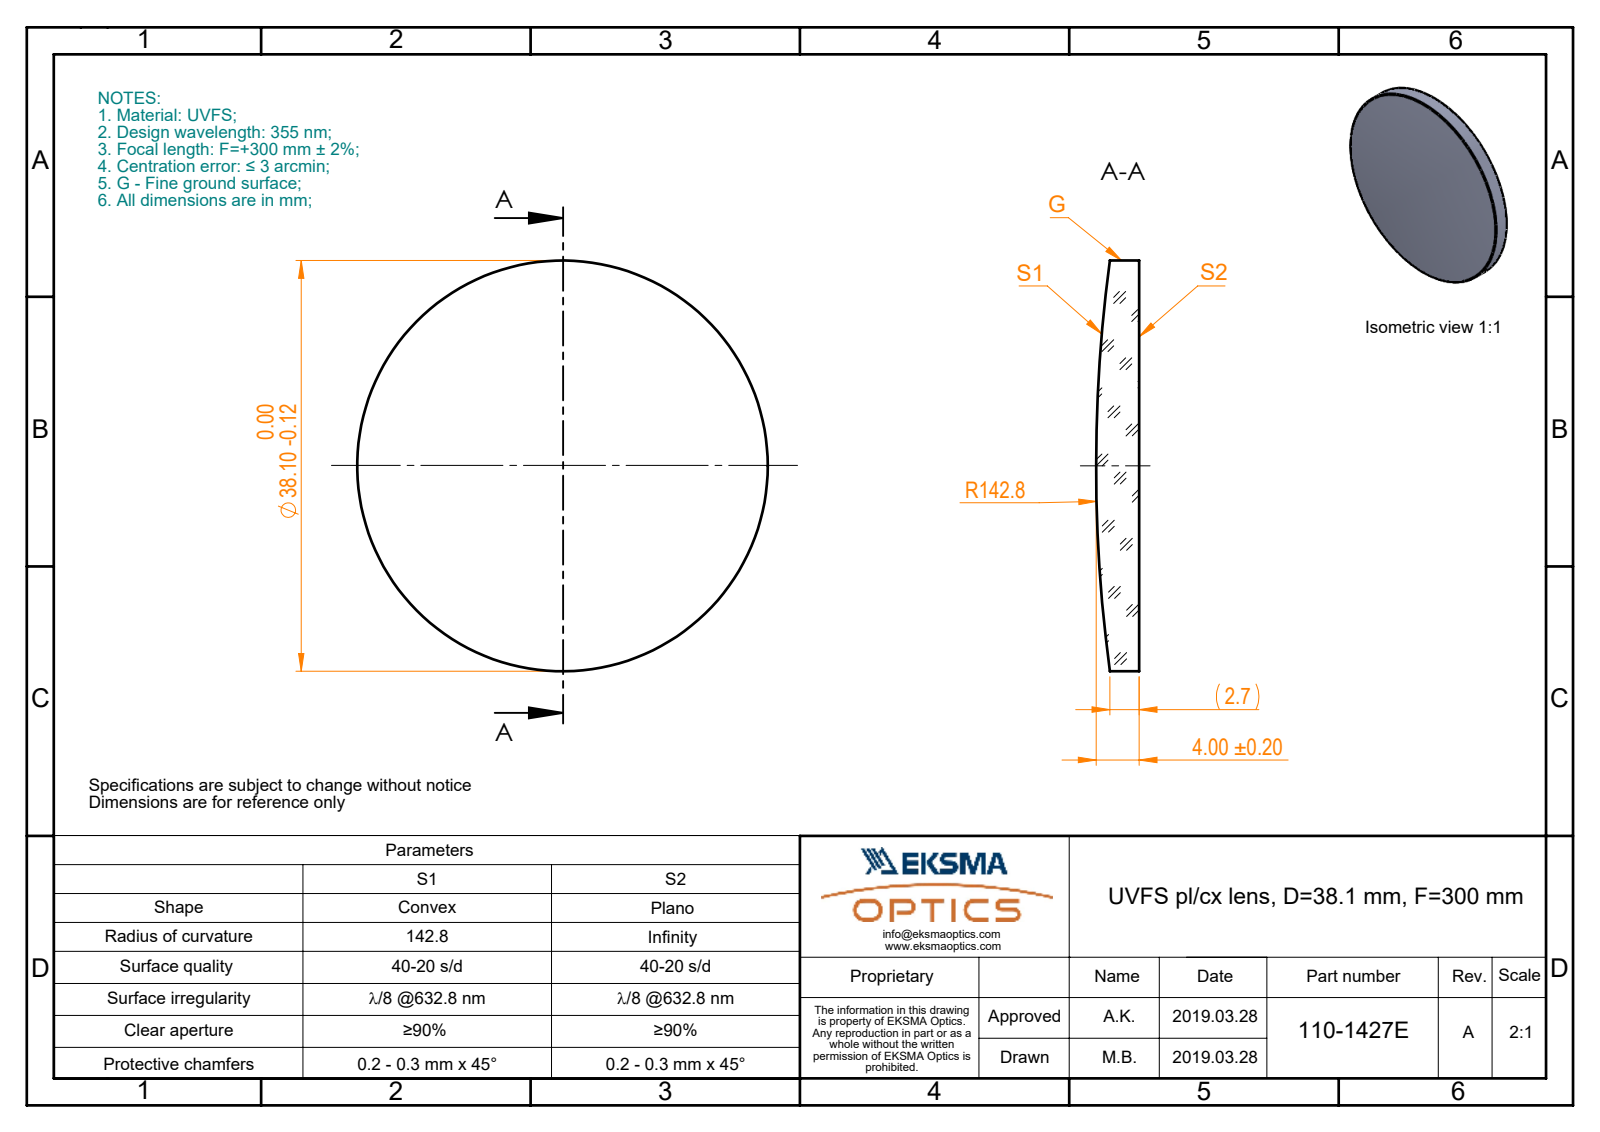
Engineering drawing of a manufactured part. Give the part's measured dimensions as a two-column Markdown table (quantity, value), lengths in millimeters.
| quantity | value |
| --- | --- |
| part name | 110-1427E UVFS pl-cx 38.1 F300 |
| STEP written by | SolidWorks 2017 (CONFIG_CONTROL_DESIGN) |
| units | millimeters |
| bodies | 1 solid, 5 faces (1 planar, 2 cylindrical, 2 other) |
| overall size | 38.1 × 38.1 × 4 |
| volume | 3 834 mm³ |
| surface area | 2 611 mm² |
| round bosses / shafts (diameter × count) | 38.1 × 1 |
